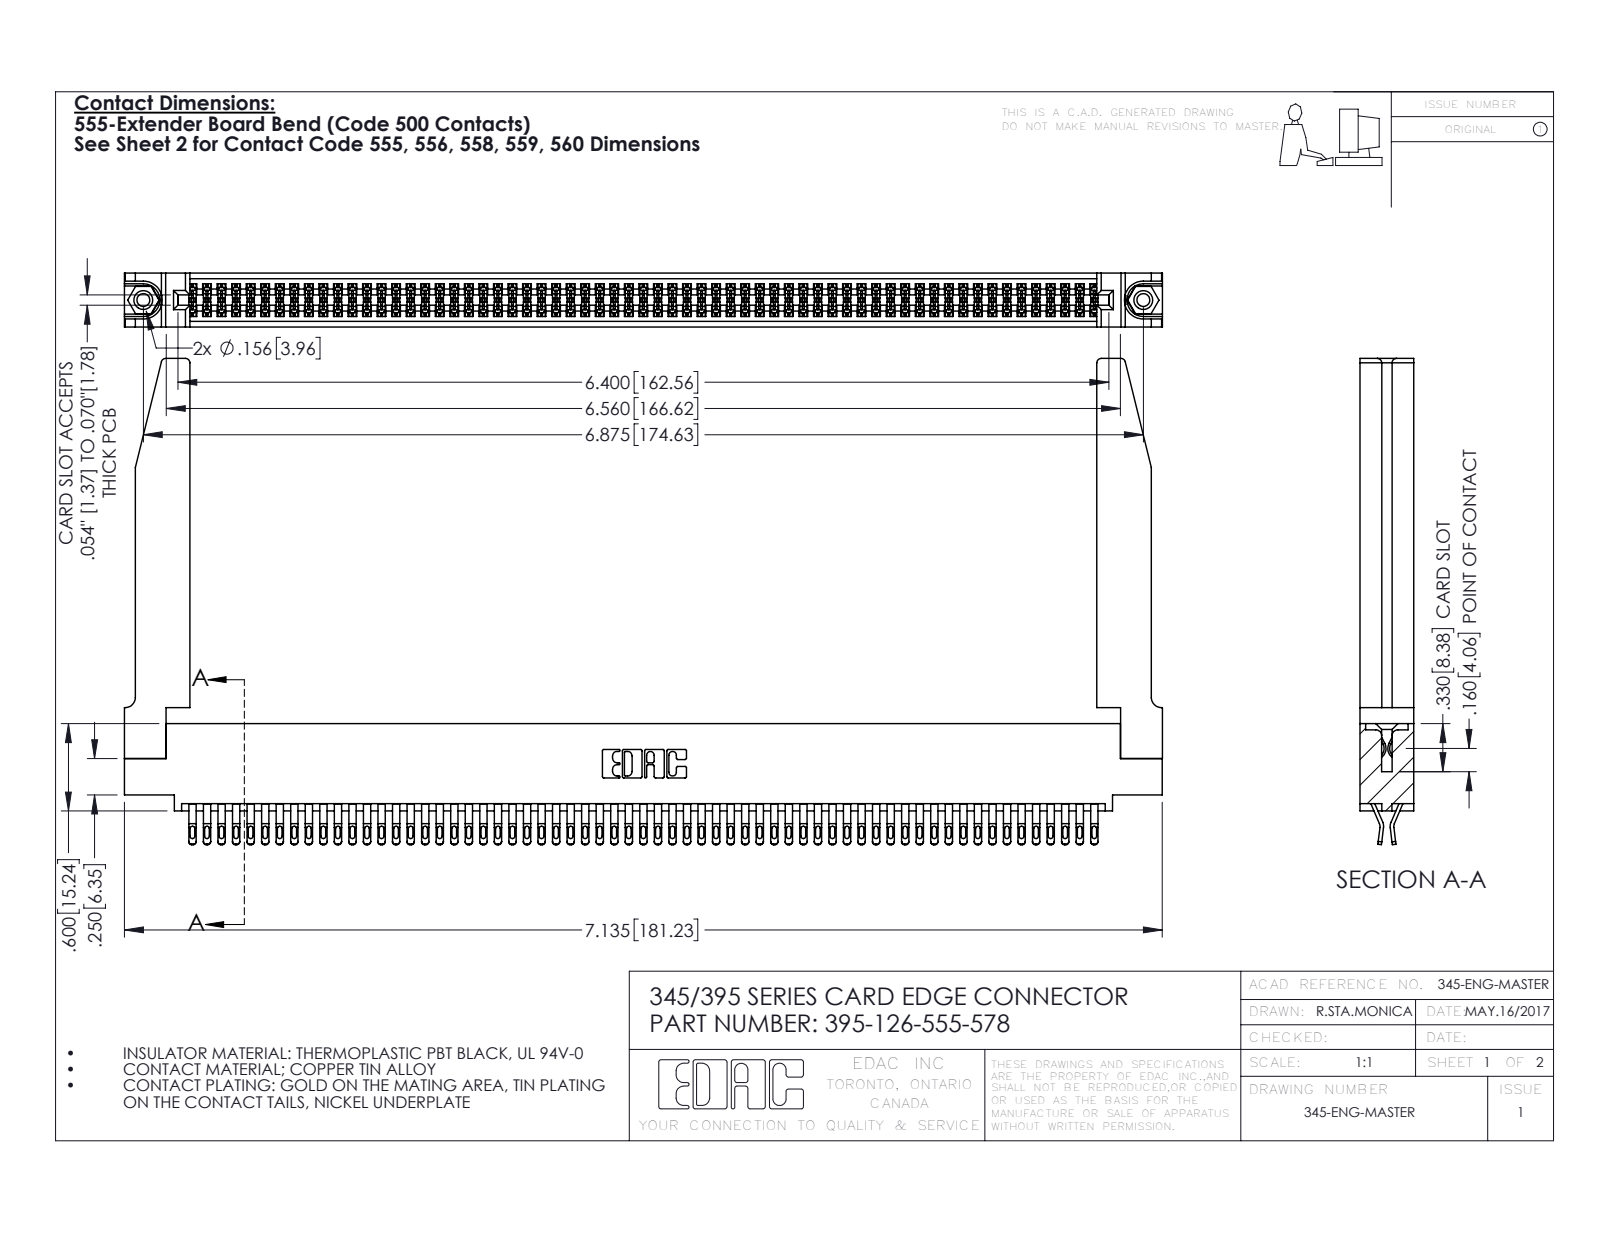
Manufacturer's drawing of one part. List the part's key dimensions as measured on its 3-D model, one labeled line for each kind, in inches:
Part name (STEP PRODUCT): 345-250-001_345-250-001-102; 395-126-555-578; 345-220-078_345-220-078; 345 Part_0.110 Offset - 0.156 Dia-TH (+1 more)
STEP written by: SolidWorks 2016 (CONFIG_CONTROL_DESIGN)
Units: inches
Bodies: 131 solids, 7420 faces (4132 planar, 3236 cylindrical, 52 other)
Overall size (bounding box): 7.136 × 3.342 × 0.37
Volume: 1.578 in³ · Surface area: 54.8 in²
Round holes (diameter × count): ⌀0.089 ×2, ⌀0.125 ×2, ⌀0.156 ×2, ⌀0.064 ×1
Round bosses / shafts (diameter × count): ⌀0.155 ×2
Partial cylindrical surfaces — rounded edges, fillets, slot ends (radius × count): R0.016 ×315, R0.02 ×252, R0.006 ×189, R0.01 ×22, R0.03 ×8, R0.007 ×6, R0.031 ×6, R0.026 ×3
Main face-to-face distances: 0.072, 0.298, 0.37, 0.025, 0.2, 0.098, 0.272, 0.225, 0.175, 0.148
Hole centre spacings: 0.27, 6.639, 6.875
